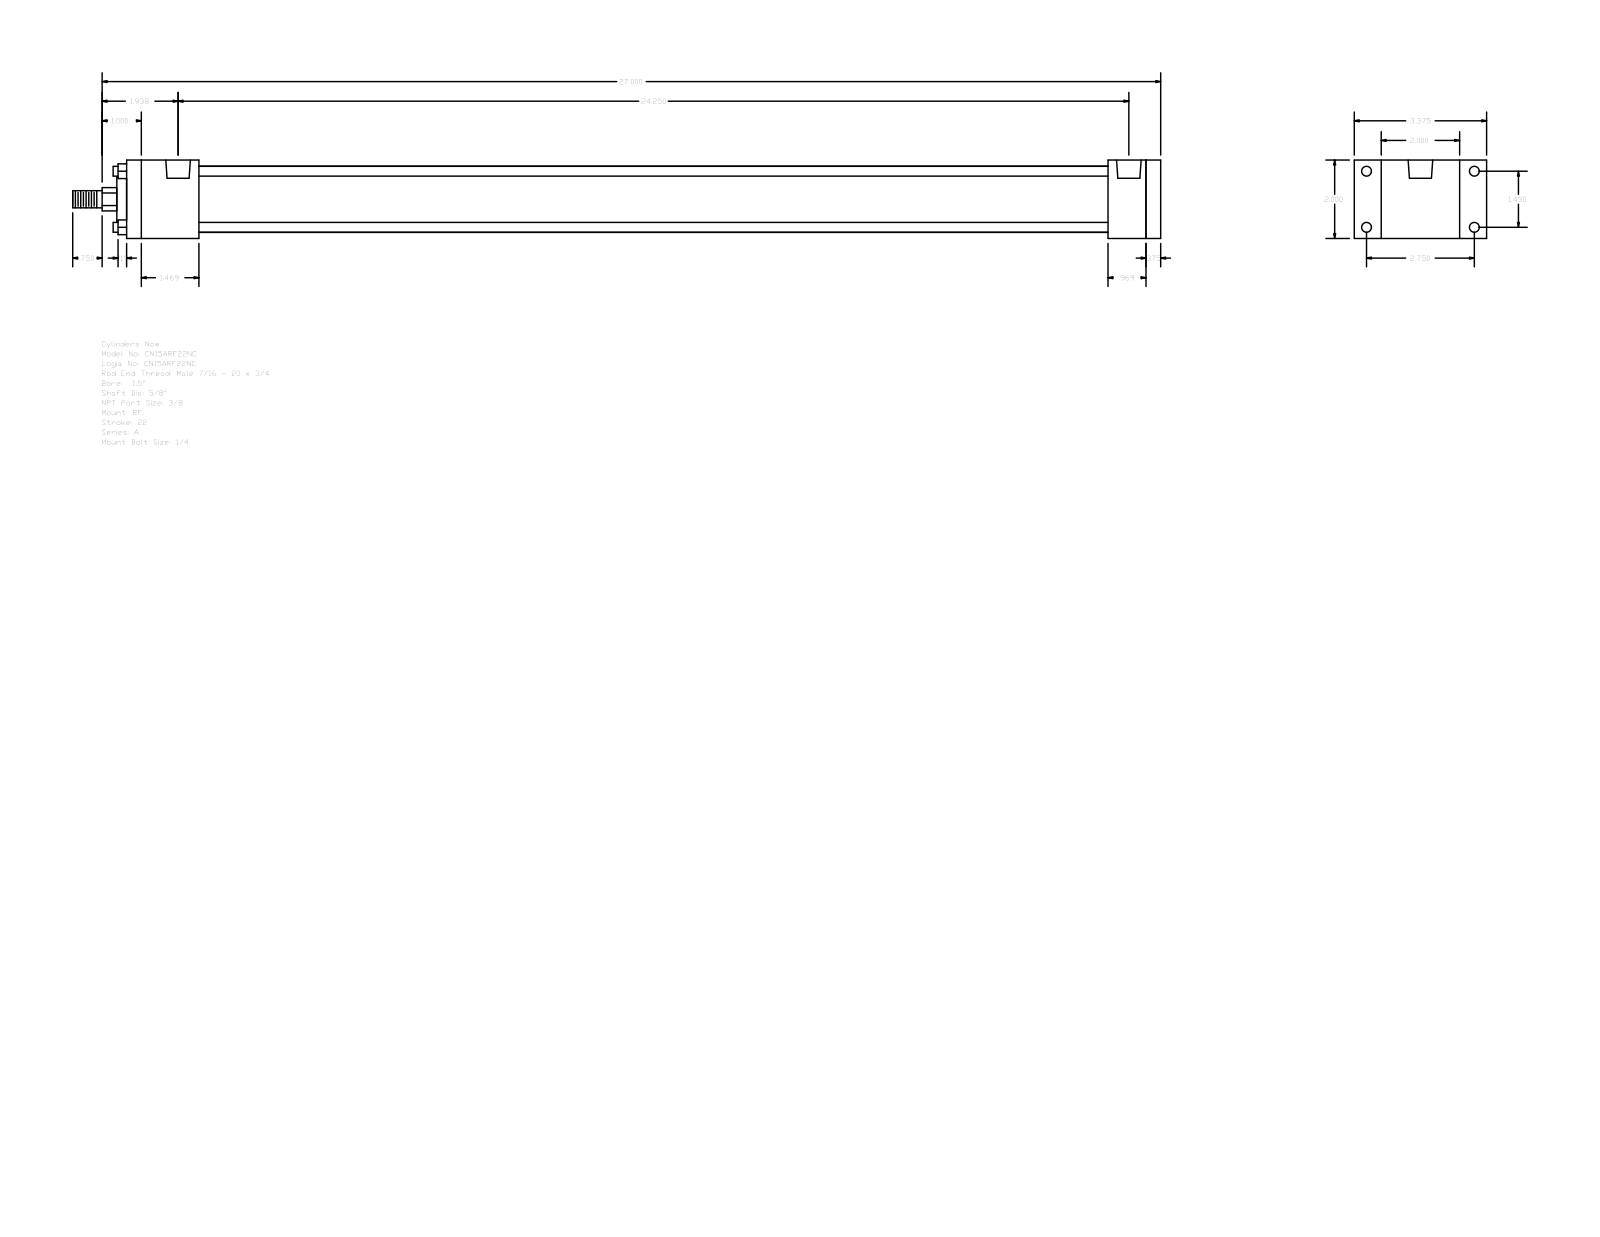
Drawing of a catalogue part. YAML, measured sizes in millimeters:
part_name: "A_RF__0150_0.625"
step_written_by: "GSSL Pune (CONFIG_CONTROL_DESIGN)"
units: millimeters
bodies: {solids: 0, faces: 92, planar: 64, cylindrical: 28, other: 0}
overall_size: [704.85, 85.72, 50.8]
round_holes:
  - {diameter: 5.56, count: 4}
  - {diameter: 6.35, count: 4}
  - {diameter: 15.93, count: 2}
round_bosses_or_shafts:
  - {diameter: 6.35, count: 4}
  - {diameter: 42.93, count: 1}
  - {diameter: 28.57, count: 1}
  - {diameter: 15.88, count: 1}
  - {diameter: 11.11, count: 1}
partial_cylinders:
  - {radius: 7.54, count: 1}
face_to_face_distances: [50.8, 9.53, 669.92, 660.39, 635.79, 24.6, 34.13, 46.83, 588.96, 613.56]
hole_center_spacings: [3.97, 36.32, 69.84, 78.72, 608.01, 611.98, 615.95]
